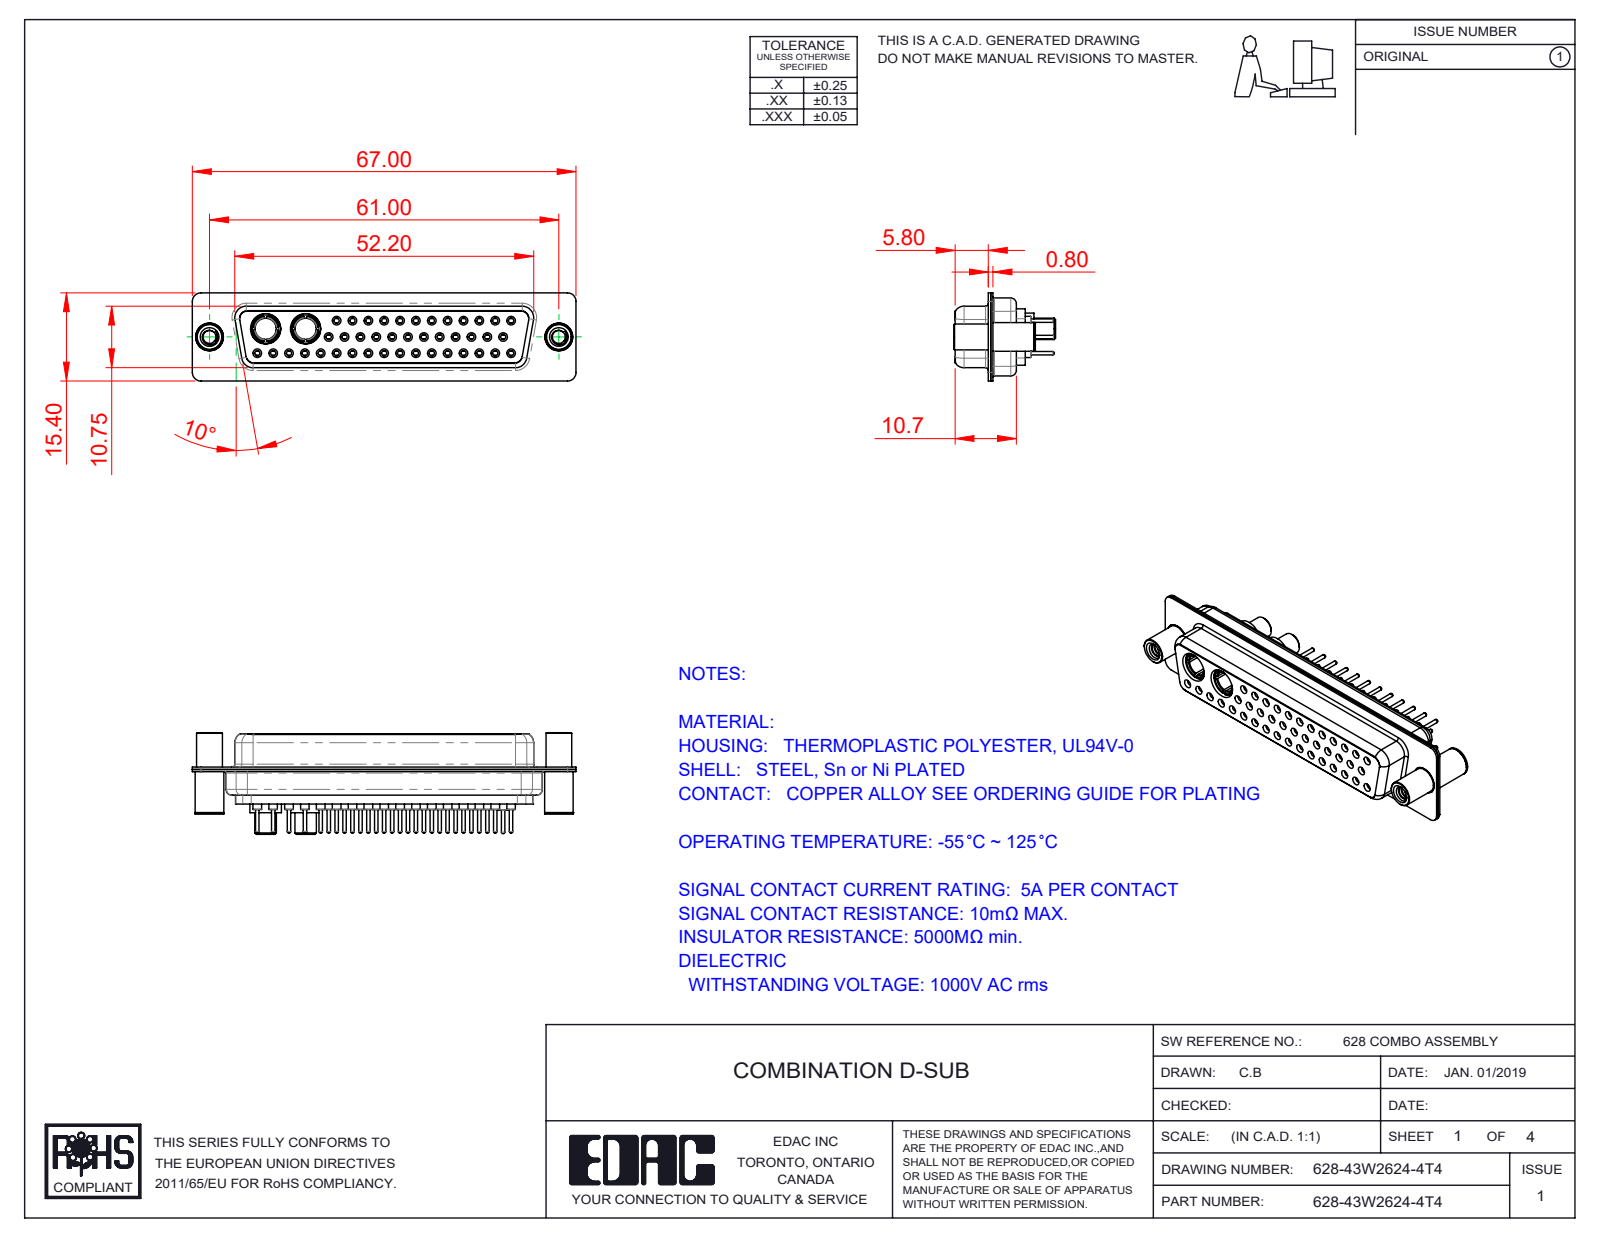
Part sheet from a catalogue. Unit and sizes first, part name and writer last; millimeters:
Units: millimetres
Overall size (bounding box): 67 × 17.75 × 15.4
Round holes (diameter × count): ⌀0.9 ×41, ⌀1.1 ×41, ⌀1.5 ×41, ⌀2 ×41, ⌀1.6 ×29, ⌀1.7 ×12, ⌀4.85 ×4, ⌀2.26 ×2, ⌀3.26 ×2, ⌀3.7 ×2, ⌀4 ×2, ⌀4.05 ×2
Round bosses / shafts (diameter × count): ⌀2.2 ×41, ⌀0.6 ×41, ⌀1.6 ×12, ⌀5.5 ×2, ⌀5.2 ×2, ⌀5 ×2, ⌀4.96 ×2, ⌀4.95 ×2
Partial cylindrical surfaces — rounded edges, fillets, slot ends (radius × count): R1.5 ×16, R1.35 ×12, R2 ×12, R1.6 ×8, R0.25 ×4, R0.5 ×4, R0.6 ×4, R0.65 ×4
Main face-to-face distances: 0.4, 6.45, 11.33, 6.05, 1.87, 10.35, 10.93, 12.25, 6.2, 5.8
Hole centre spacings: 2.77, 3.16, 5.54, 8.31, 11.08, 13.85, 16.62, 19.39
Volume: 7 336 mm³ · Surface area: 15 153 mm²
Bodies: 50 solids, 2770 faces (746 planar, 1014 cylindrical, 1010 other)
Part name (STEP PRODUCT): 628-43W2624-4T4; Power Socket_40A S; 628Combo Contact Row 1_24; 628Combo Contact Row 3_24 (+5 more)
STEP written by: SolidWorks 2016 (CONFIG_CONTROL_DESIGN)
